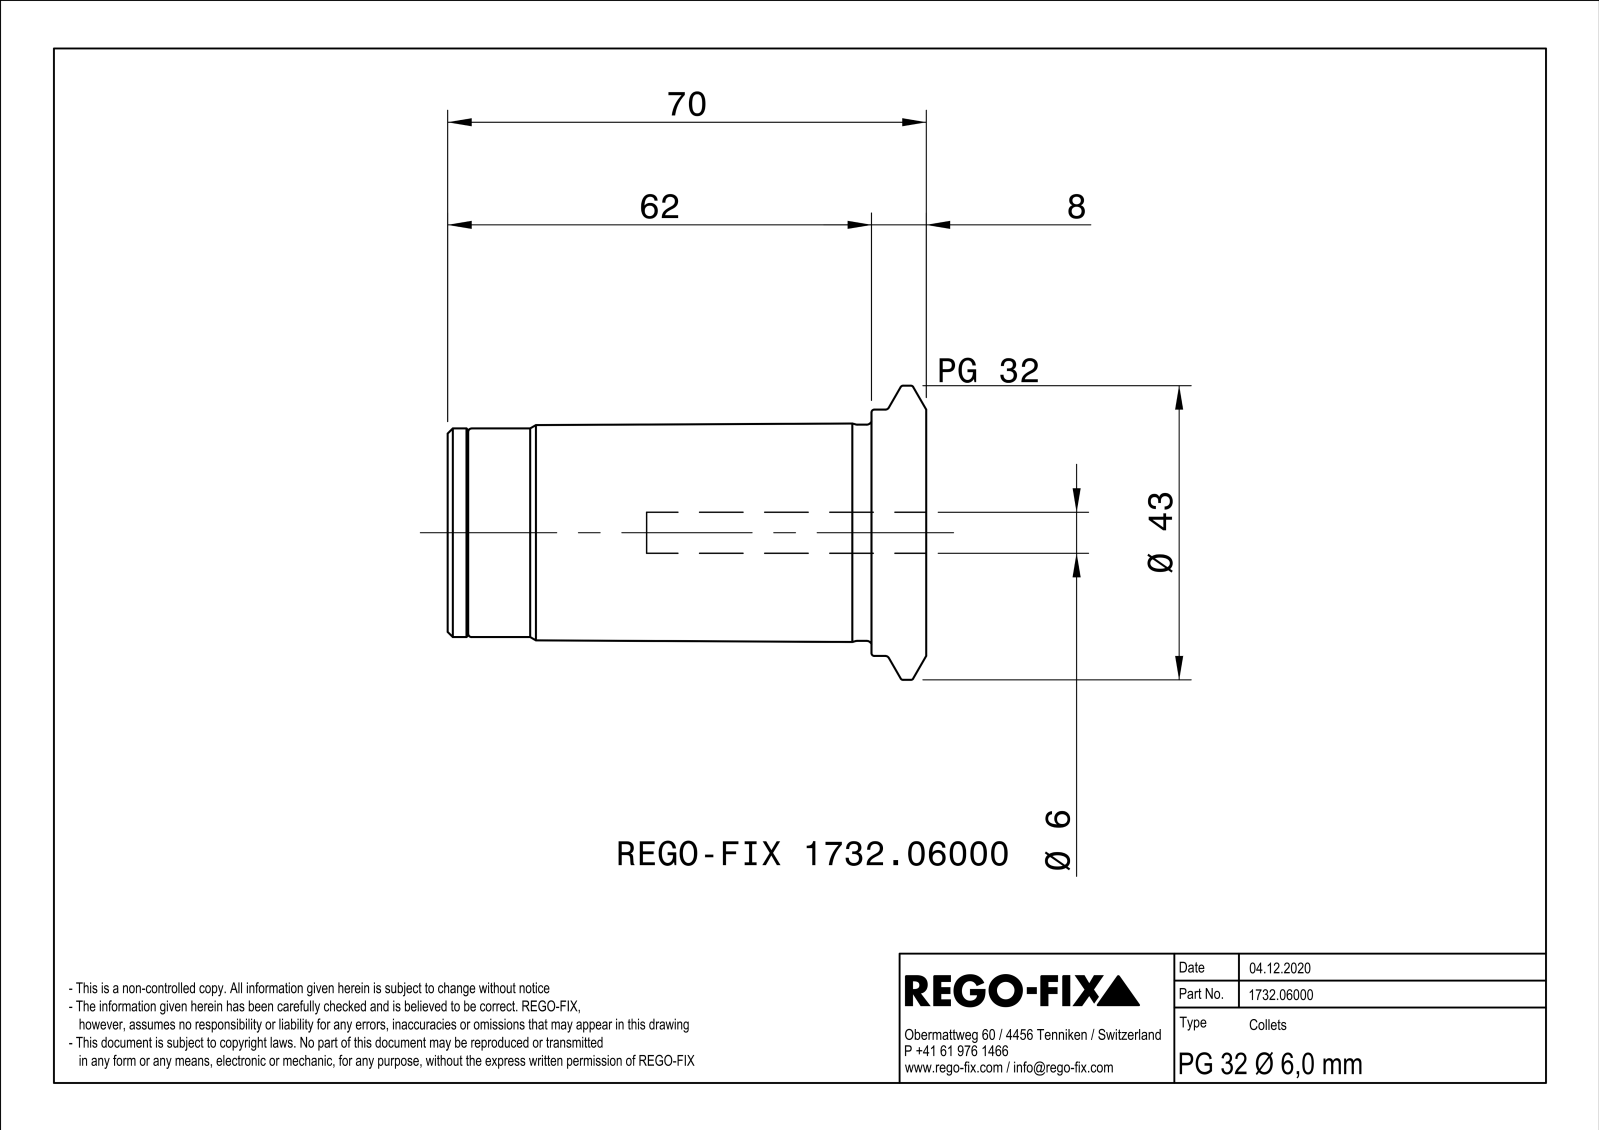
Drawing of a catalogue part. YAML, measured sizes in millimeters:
part_name: "NOCUT"
step_written_by: "SIEMENS PLM Software Solid Edge ST10 (AUTOMOTIVE_DESIGN)"
units: millimeters
bodies: {solids: 1, faces: 127, planar: 31, cylindrical: 41, other: 55}
overall_size: [70, 43, 42.99]
volume: 48496
surface_area: 16593
round_holes:
  - {diameter: 4, count: 3}
  - {diameter: 6, count: 1}
  - {diameter: 8.92, count: 1}
  - {diameter: 10.5, count: 1}
  - {diameter: 15.5, count: 1}
  - {diameter: 26.92, count: 1}
  - {diameter: 28.5, count: 1}
round_bosses_or_shafts:
  - {diameter: 43, count: 1}
  - {diameter: 36, count: 1}
  - {diameter: 31.6, count: 1}
  - {diameter: 30.5, count: 1}
  - {diameter: 26.5, count: 1}
  - {diameter: 21, count: 1}
partial_cylinders:
  - {radius: 2, count: 6}
  - {radius: 3.5, count: 3}
  - {radius: 3.98, count: 1}
  - {radius: 4.75, count: 1}
  - {radius: 8.75, count: 1}
face_to_face_distances: [1, 70, 58, 12, 59, 11, 8, 60, 2, 10]
hole_center_spacings: [7.75, 13.42, 13.43]
